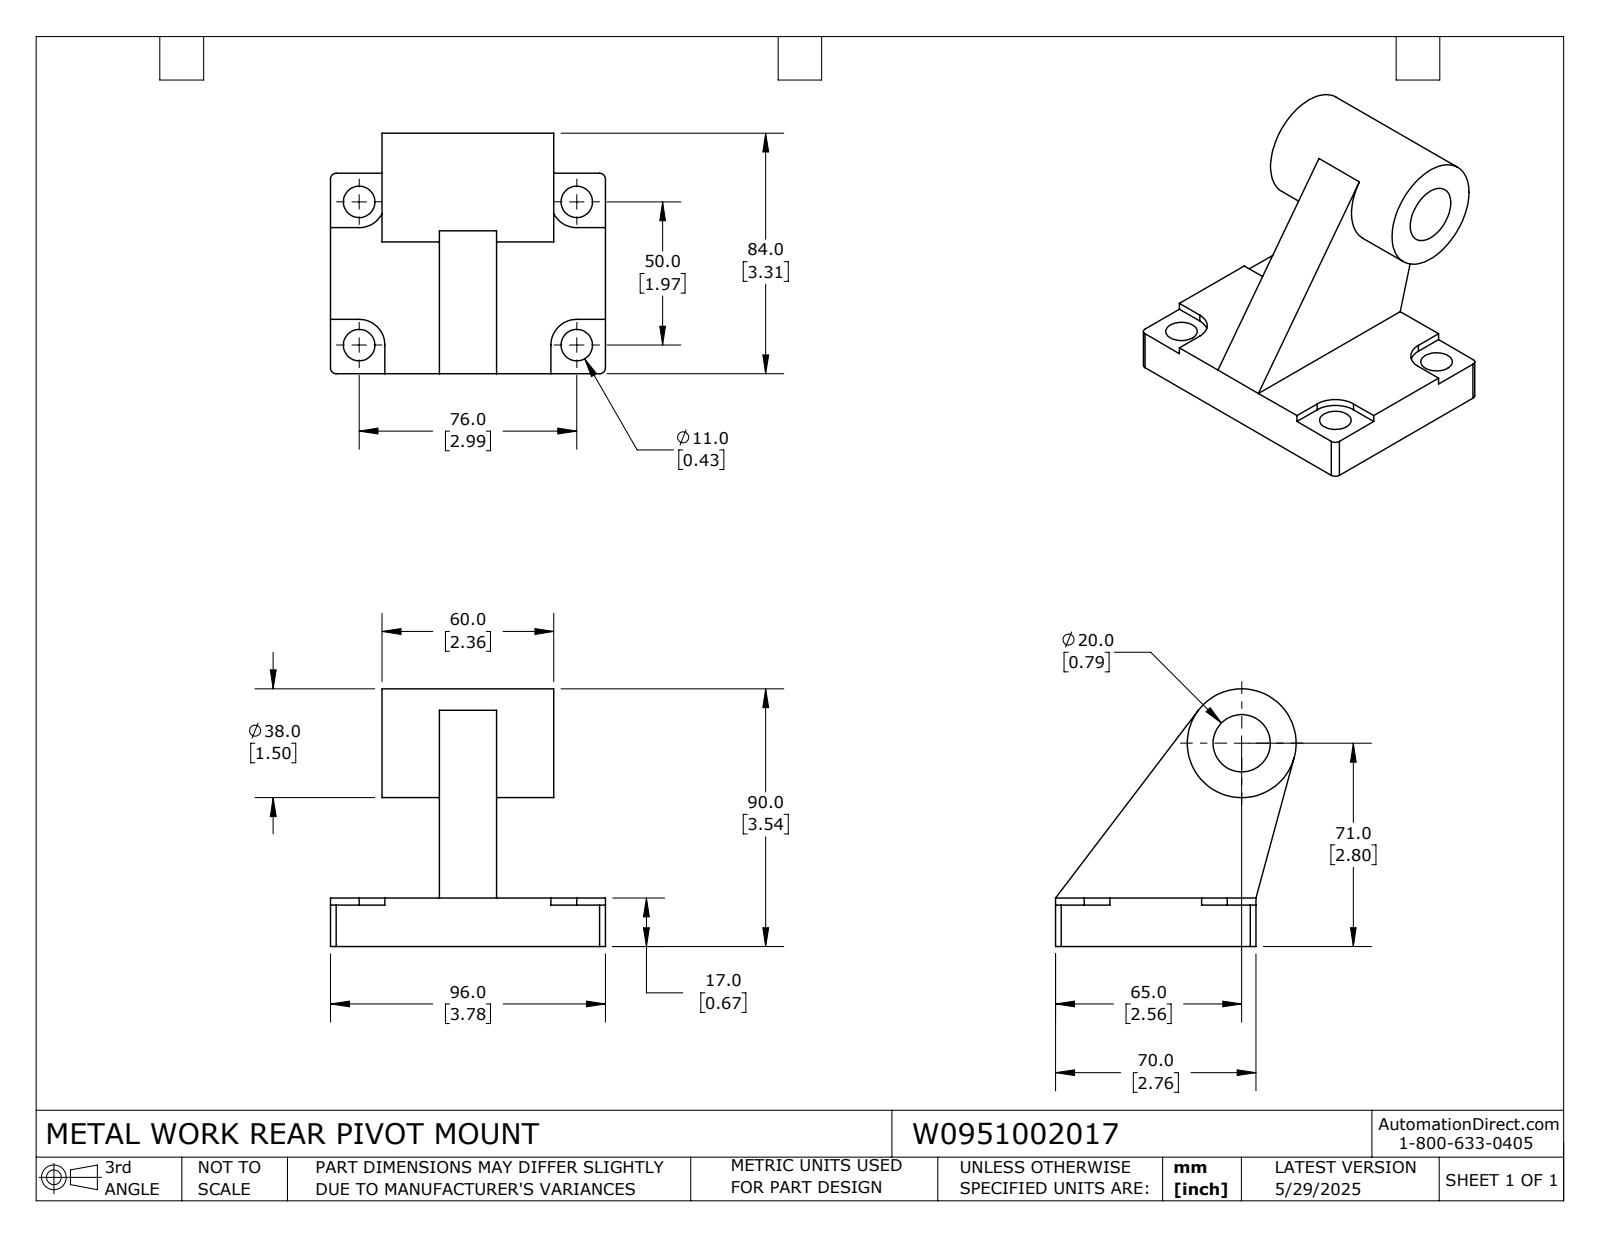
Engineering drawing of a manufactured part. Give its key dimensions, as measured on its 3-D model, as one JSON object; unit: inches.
{"part_name": "W0951002017", "step_written_by": "SolidWorks 2024 (CONFIG_CONTROL_DESIGN)", "units": "inches", "bodies": {"solids": 1, "faces": 50, "planar": 30, "cylindrical": 20, "other": 0}, "overall_size": [3.78, 3.543, 3.307], "volume_in3": 12.48, "surface_area_in2": 58.74, "round_holes": [[0.433, 4], [0.787, 1]], "round_bosses_or_shafts": [[1.496, 1]], "partial_cylinders_radius": [[0.079, 4], [0.354, 4]], "face_to_face_distances": [0.787, 0.669, 2.283, 1.496, 0.709, 3.071, 1.575, 2.756, 3.78, 0.571], "hole_center_spacings": [1.969, 2.992, 3.581]}
